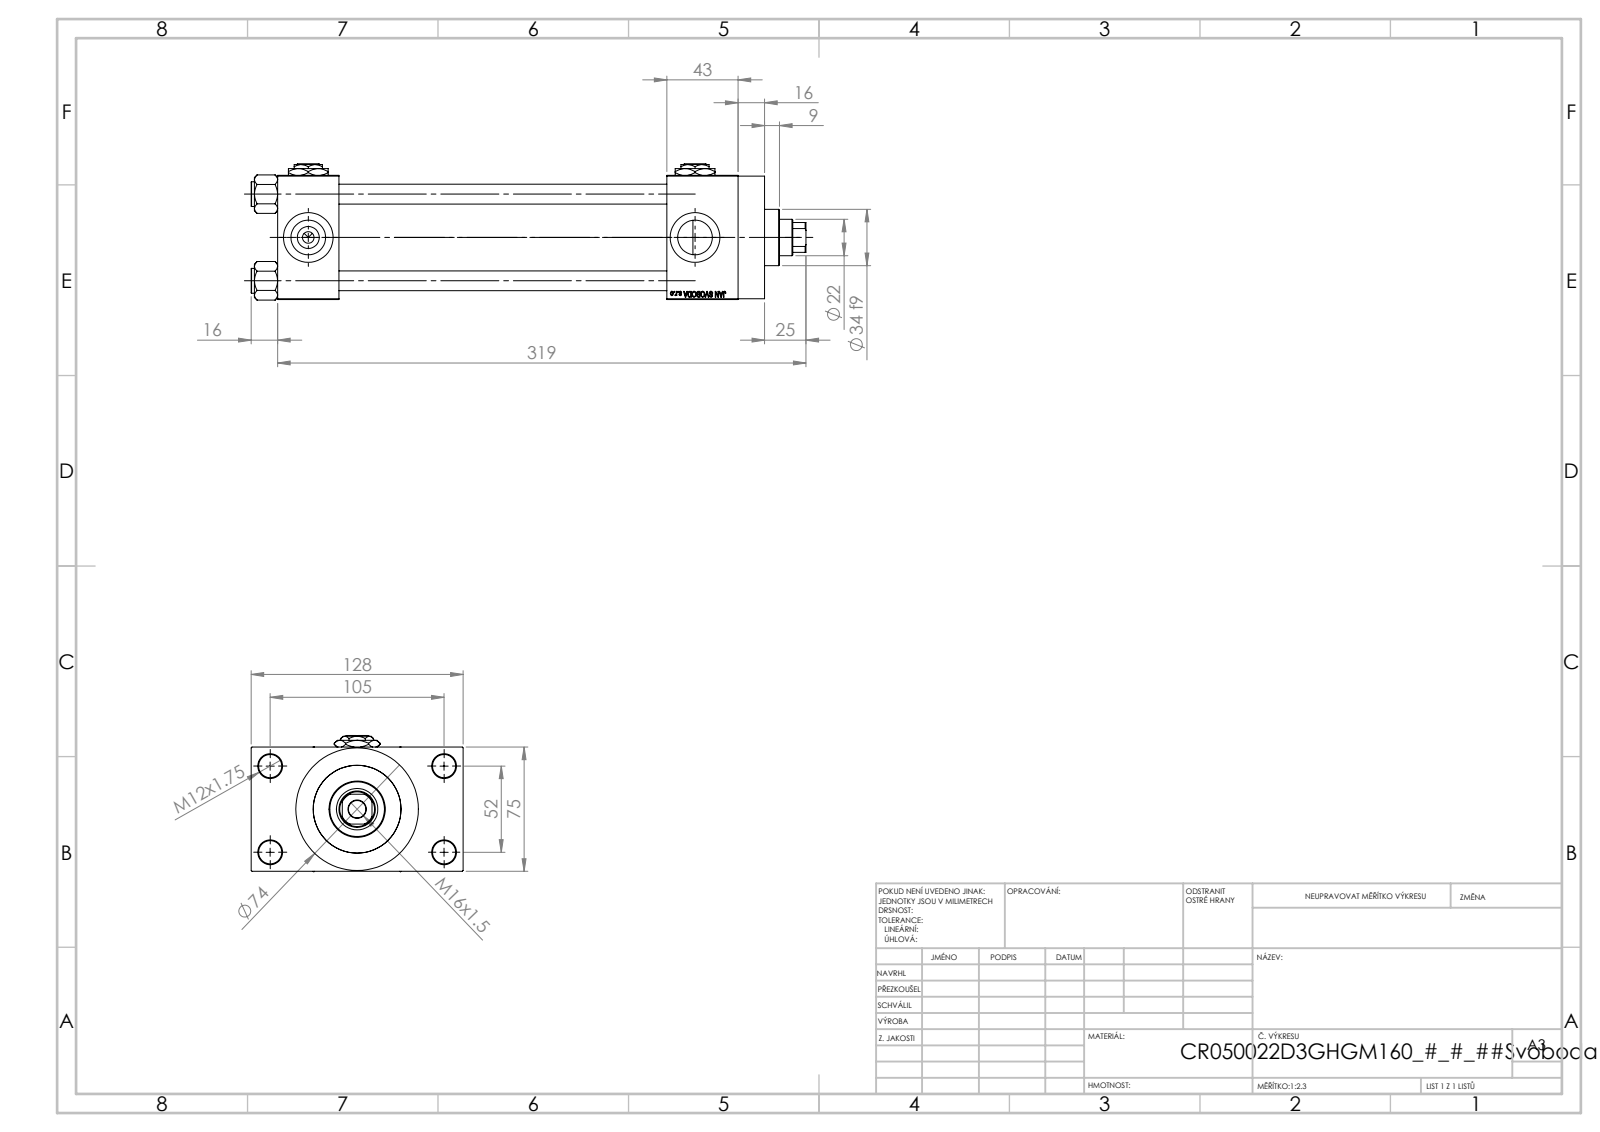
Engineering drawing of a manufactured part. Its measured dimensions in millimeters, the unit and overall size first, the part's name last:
Units: millimetres
Overall size (bounding box): 335 × 128 × 82.27
Round holes (diameter × count): ⌀12 ×4, ⌀14 ×4, ⌀20.96 ×4, ⌀30 ×4, ⌀7 ×3, ⌀10.5 ×1, ⌀22 ×1, ⌀25 ×1, ⌀41 ×1, ⌀50 ×1, ⌀53 ×1
Round bosses / shafts (diameter × count): ⌀15 ×4, ⌀74 ×1, ⌀56 ×1, ⌀34 ×1
Partial cylindrical surfaces — rounded edges, fillets, slot ends (radius × count): R10.5 ×1
Main face-to-face distances: 75, 198, 37, 235, 26.5, 278, 241, 43, 101.5, 16
Hole centre spacings: 26.35, 36.98, 52.3, 58.43, 58.59, 78.65, 94.37, 52
Volume: 979 616 mm³ · Surface area: 248 330 mm²
Bodies: 13 solids, 1204 faces (545 planar, 99 cylindrical, 560 other)
Part name (STEP PRODUCT): V215_VC_A; Zatka_pro_OIL_PORT; V215CR_VCP_D; V215CR_D_TYCINKA (+2 more)
STEP written by: SolidWorks 2019 (CONFIG_CONTROL_DESIGN)
